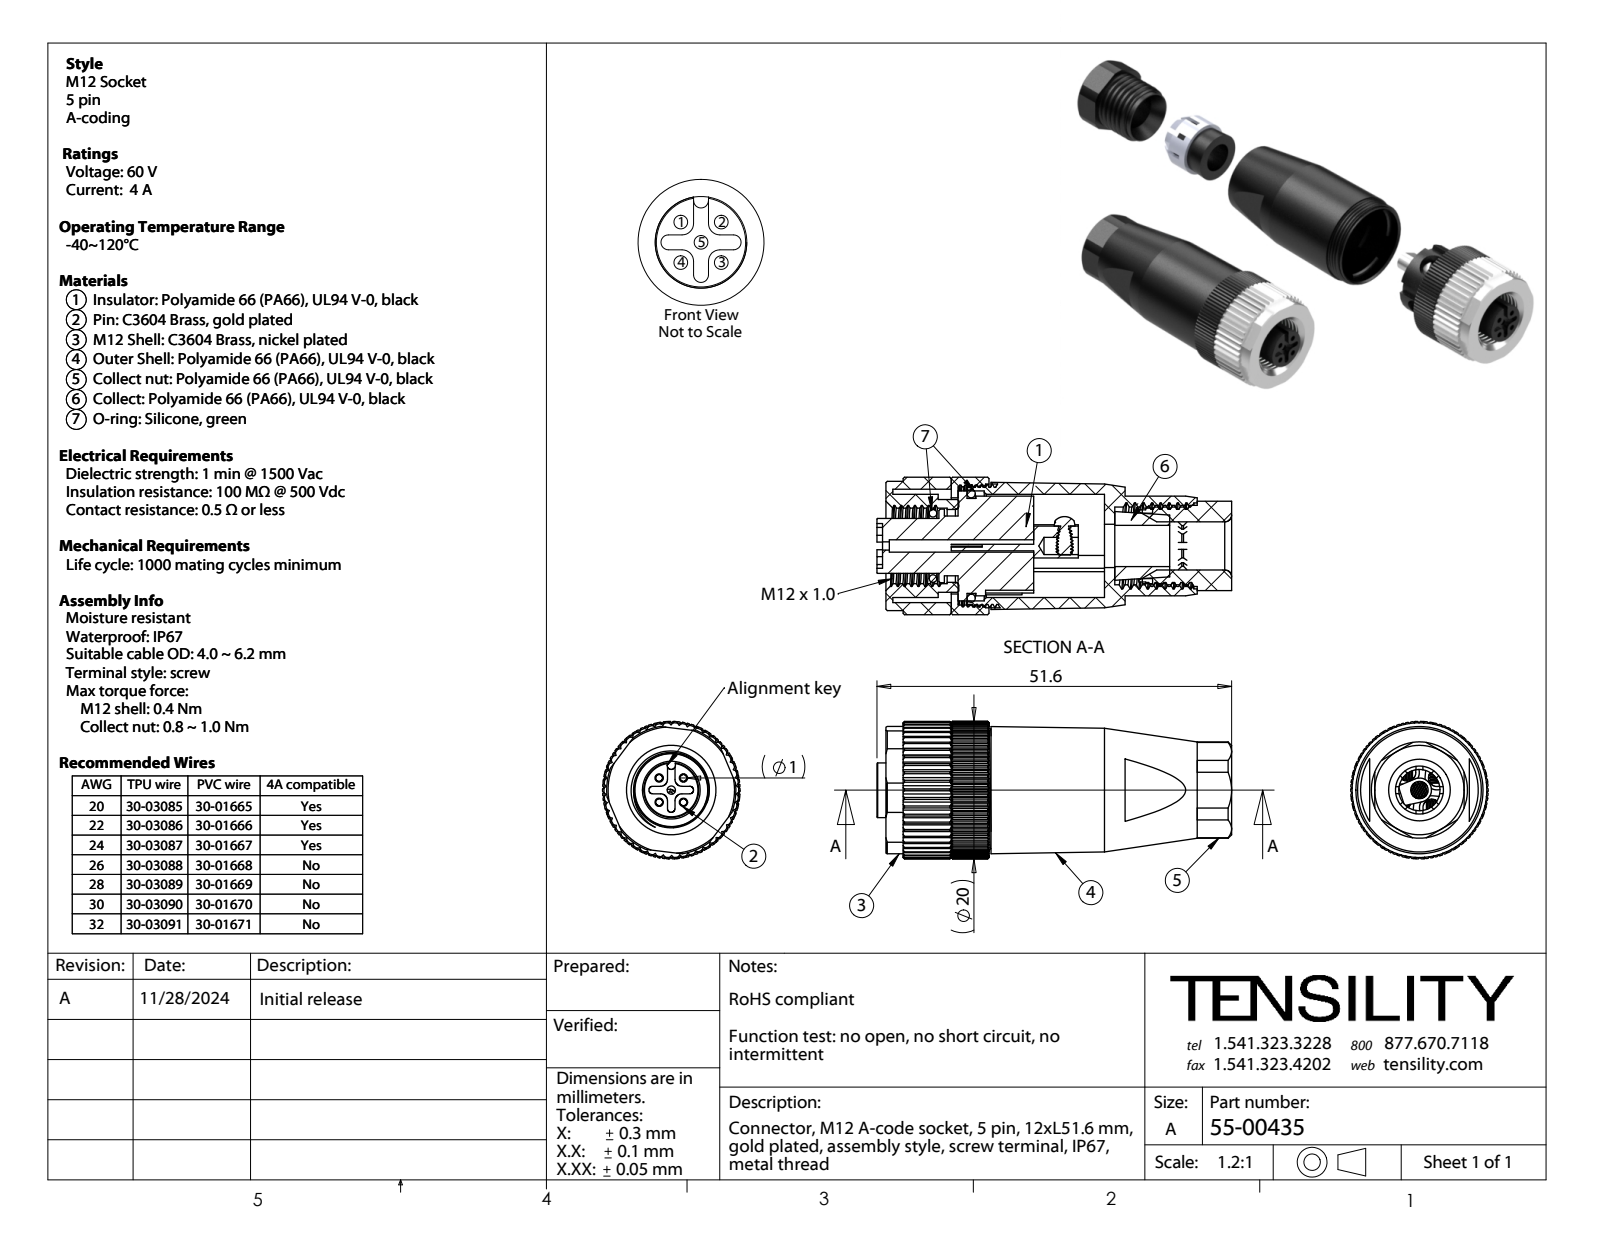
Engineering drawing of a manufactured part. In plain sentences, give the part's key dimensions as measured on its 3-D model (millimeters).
The part is named "55-00435-03; 55-00435-01; 55-00435-06; 55-00435-02 (+7 more)". Its 3-D file was written by "SolidWorks 2021 (CONFIG_CONTROL_DESIGN)". It is 18 solids with 1517 faces: 544 planar, 528 cylindrical and 445 other. Overall it measures 51.6 by 20 by 20 millimeters. Its volume is 8 434 cubic millimeters and its surface area 13 893 square millimeters. Round holes: 9 of diameter 2.5, 5 of diameter 1, 5 of diameter 1.2, 5 of diameter 1.8, 5 of diameter 2.05, 4 of diameter 5, 1 of diameter 6, 1 of diameter 6.3, 1 of diameter 7, 1 of diameter 9.5, 1 of diameter 10.6, 1 of diameter 11. Round bosses or shafts: 5 of diameter 3.5, 5 of diameter 2.4, 1 of diameter 17.8, 1 of diameter 17.03, 1 of diameter 17, 1 of diameter 14.5, 1 of diameter 14, 1 of diameter 13.8. Partial cylindrical surfaces (rounded edges, fillets, slot ends): 5 of radius 1.75, 4 of radius 1, 3 of radius 0.55, 1 of radius 0.6, 1 of radius 5.3, 1 of radius 6.45, 1 of radius 6.5, 1 of radius 9.4. The main face-to-face distances are 1, 9.5, 11.8, 23.8, 22.3, 12, 13.44, 21.5, 31.8, 10.5. The hole center spacings are 5.14, 5.13, 0.8, 2.5, 3.12, 3.54, 3.62, 4.34.
